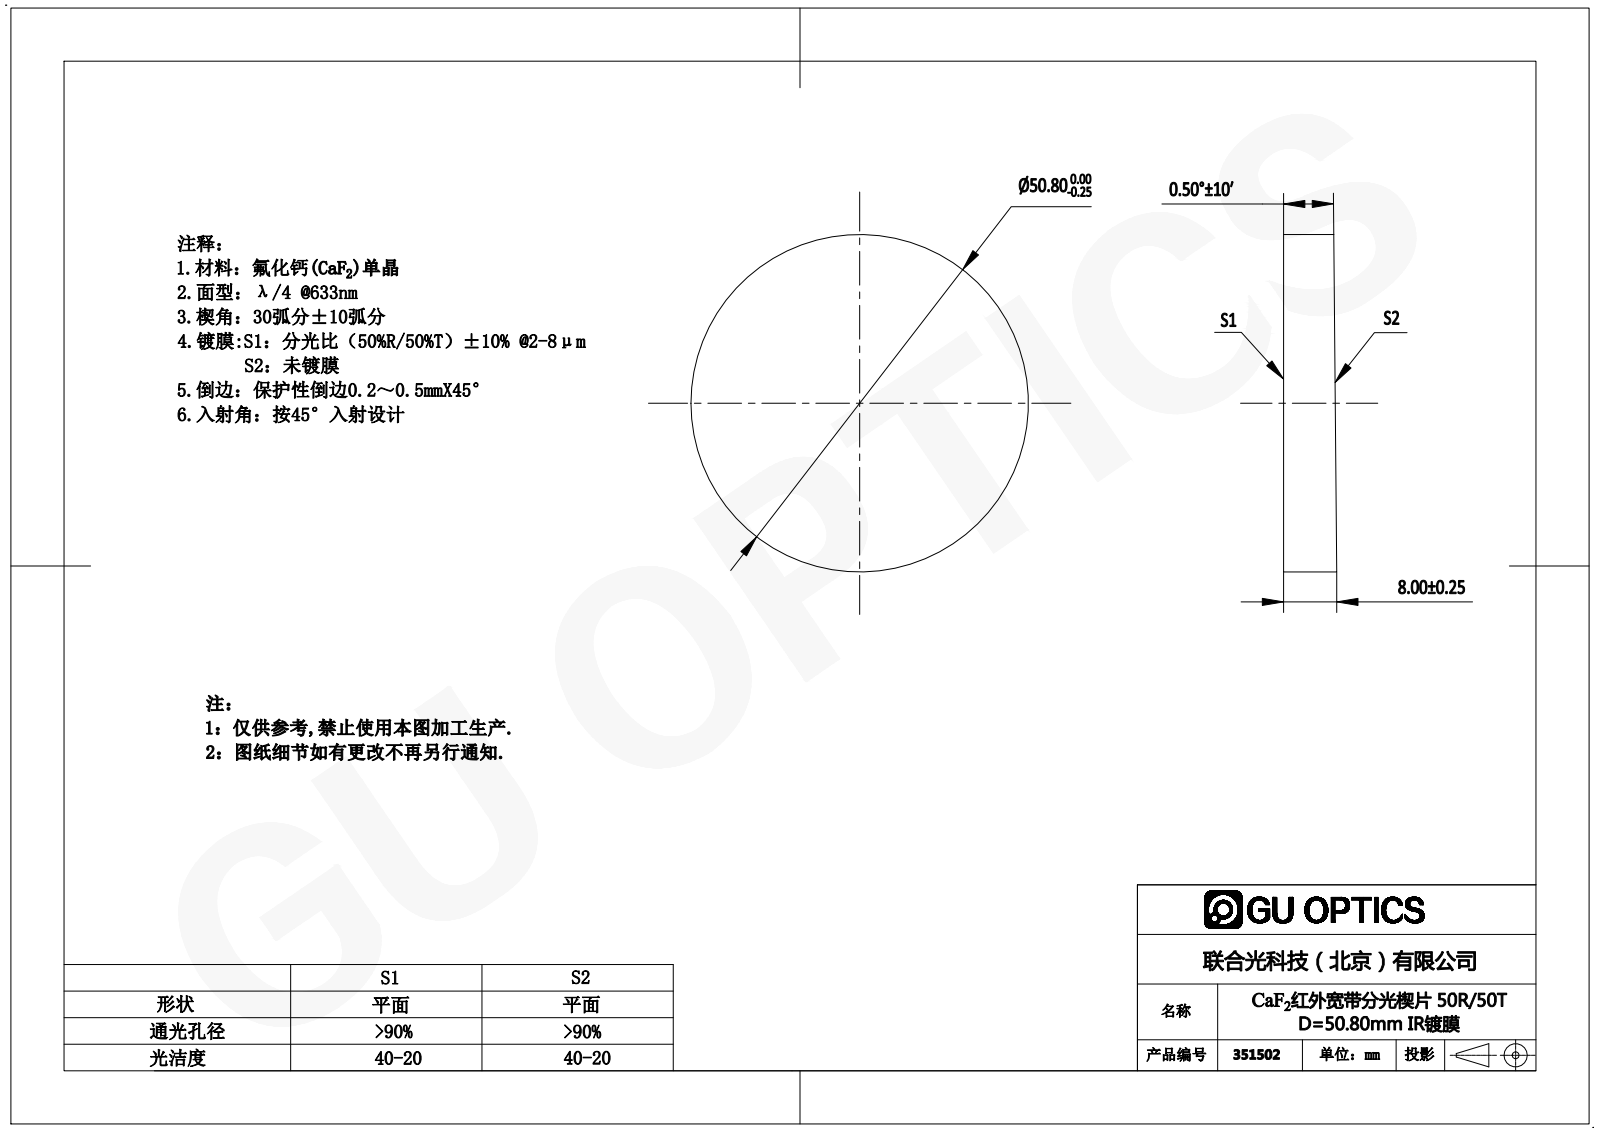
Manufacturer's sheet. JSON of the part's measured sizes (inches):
{"part_name": "351502", "step_written_by": "SolidWorks 2016 (AUTOMOTIVE_DESIGN)", "units": "inches", "bodies": {"solids": 1, "faces": 4, "planar": 2, "cylindrical": 2, "other": 0}, "overall_size": [2, 2, 0.315], "volume_in3": 0.962, "surface_area_in2": 8.207, "round_bosses_or_shafts": [[2, 1]]}
